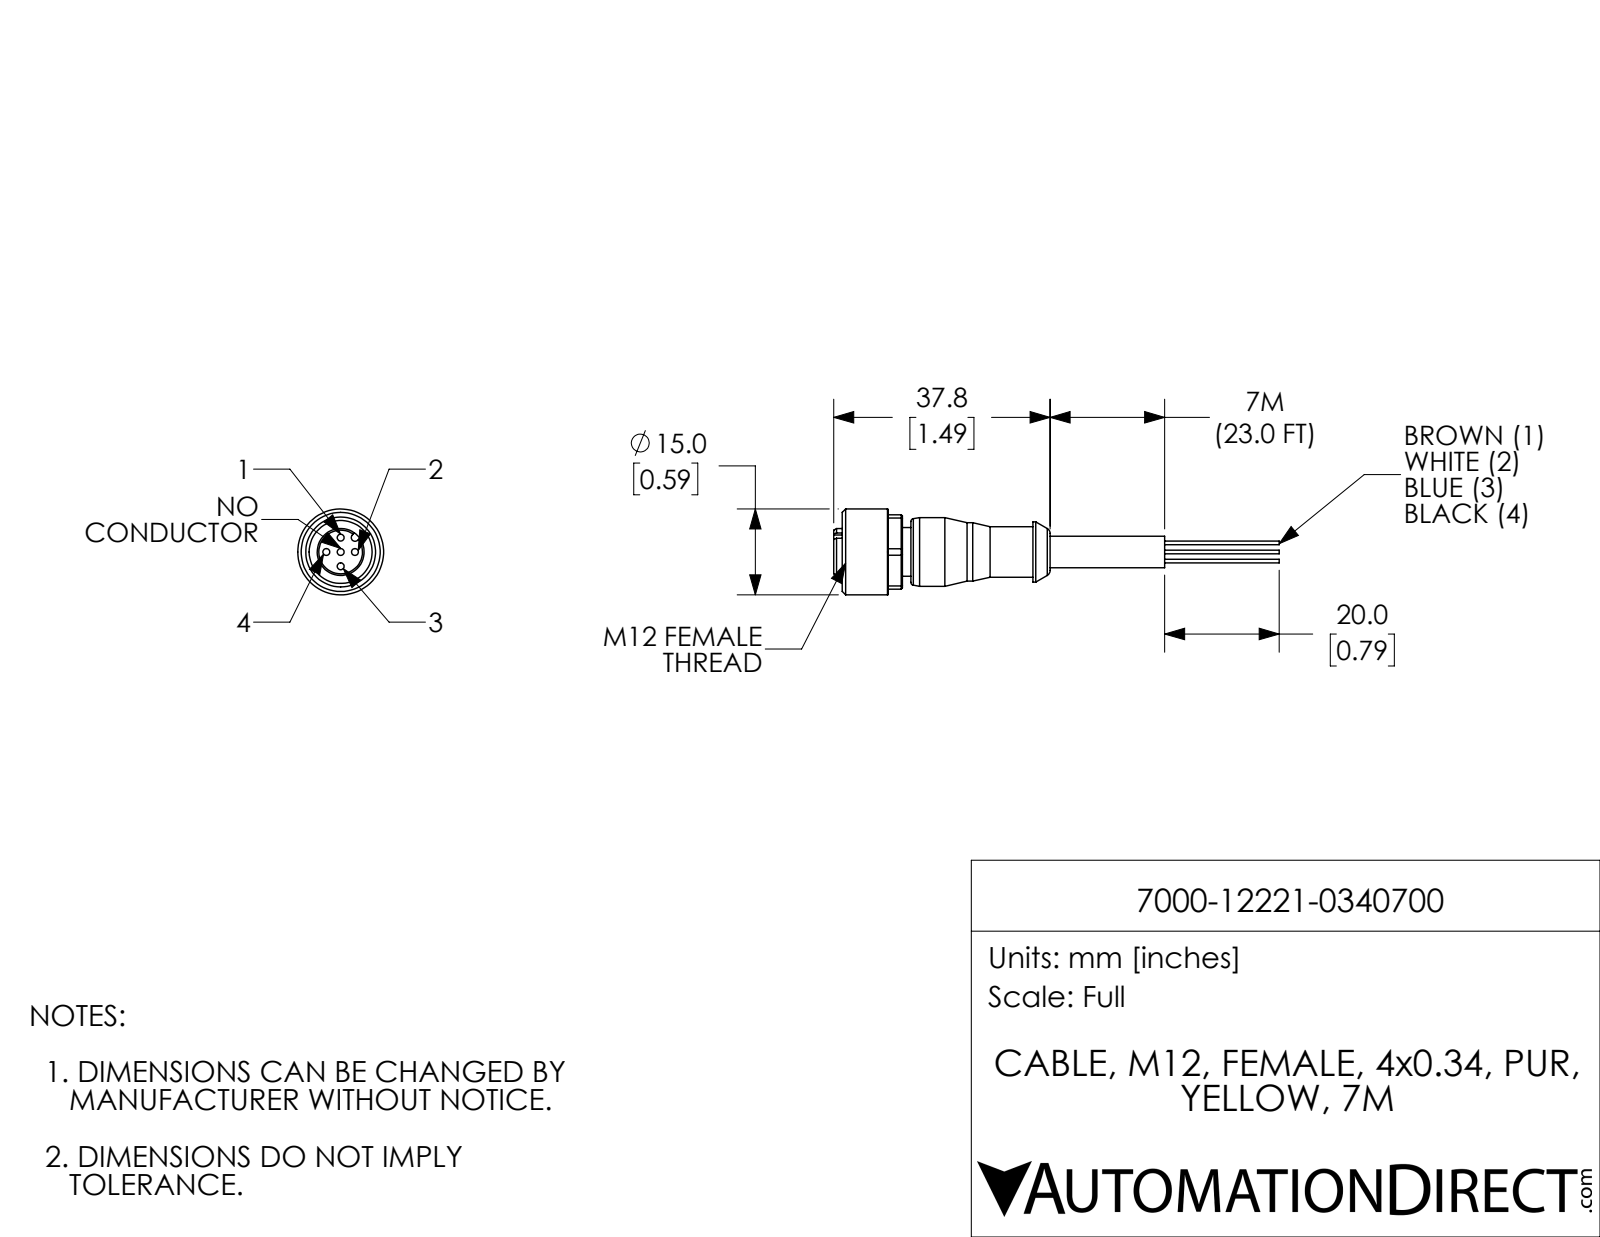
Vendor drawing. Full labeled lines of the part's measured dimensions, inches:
Part name (STEP PRODUCT): 7000-12221-0340700
STEP written by: SolidWorks 2021 (CONFIG_CONTROL_DESIGN)
Units: inches
Bodies: 1 solid, 103 faces (33 planar, 43 cylindrical, 27 other)
Overall size (bounding box): 3.063 × 0.591 × 0.591
Volume: 0.247 in³ · Surface area: 4.386 in²
Round holes (diameter × count): ⌀0.047 ×5, ⌀0.433 ×1
Round bosses / shafts (diameter × count): ⌀0.026 ×4, ⌀0.591 ×1, ⌀0.472 ×1, ⌀0.413 ×1, ⌀0.402 ×1, ⌀0.346 ×1, ⌀0.335 ×1, ⌀0.323 ×1
Partial cylindrical surfaces — rounded edges, fillets, slot ends (radius × count): R0.026 ×1, R0.283 ×1
Main face-to-face distances: 0.472, 0.059, 0.118, 0.512, 0.354, 1.016, 0.295, 0.413, 0.098, 0.531
Hole centre spacings: 0.098, 0.139, 0.197
